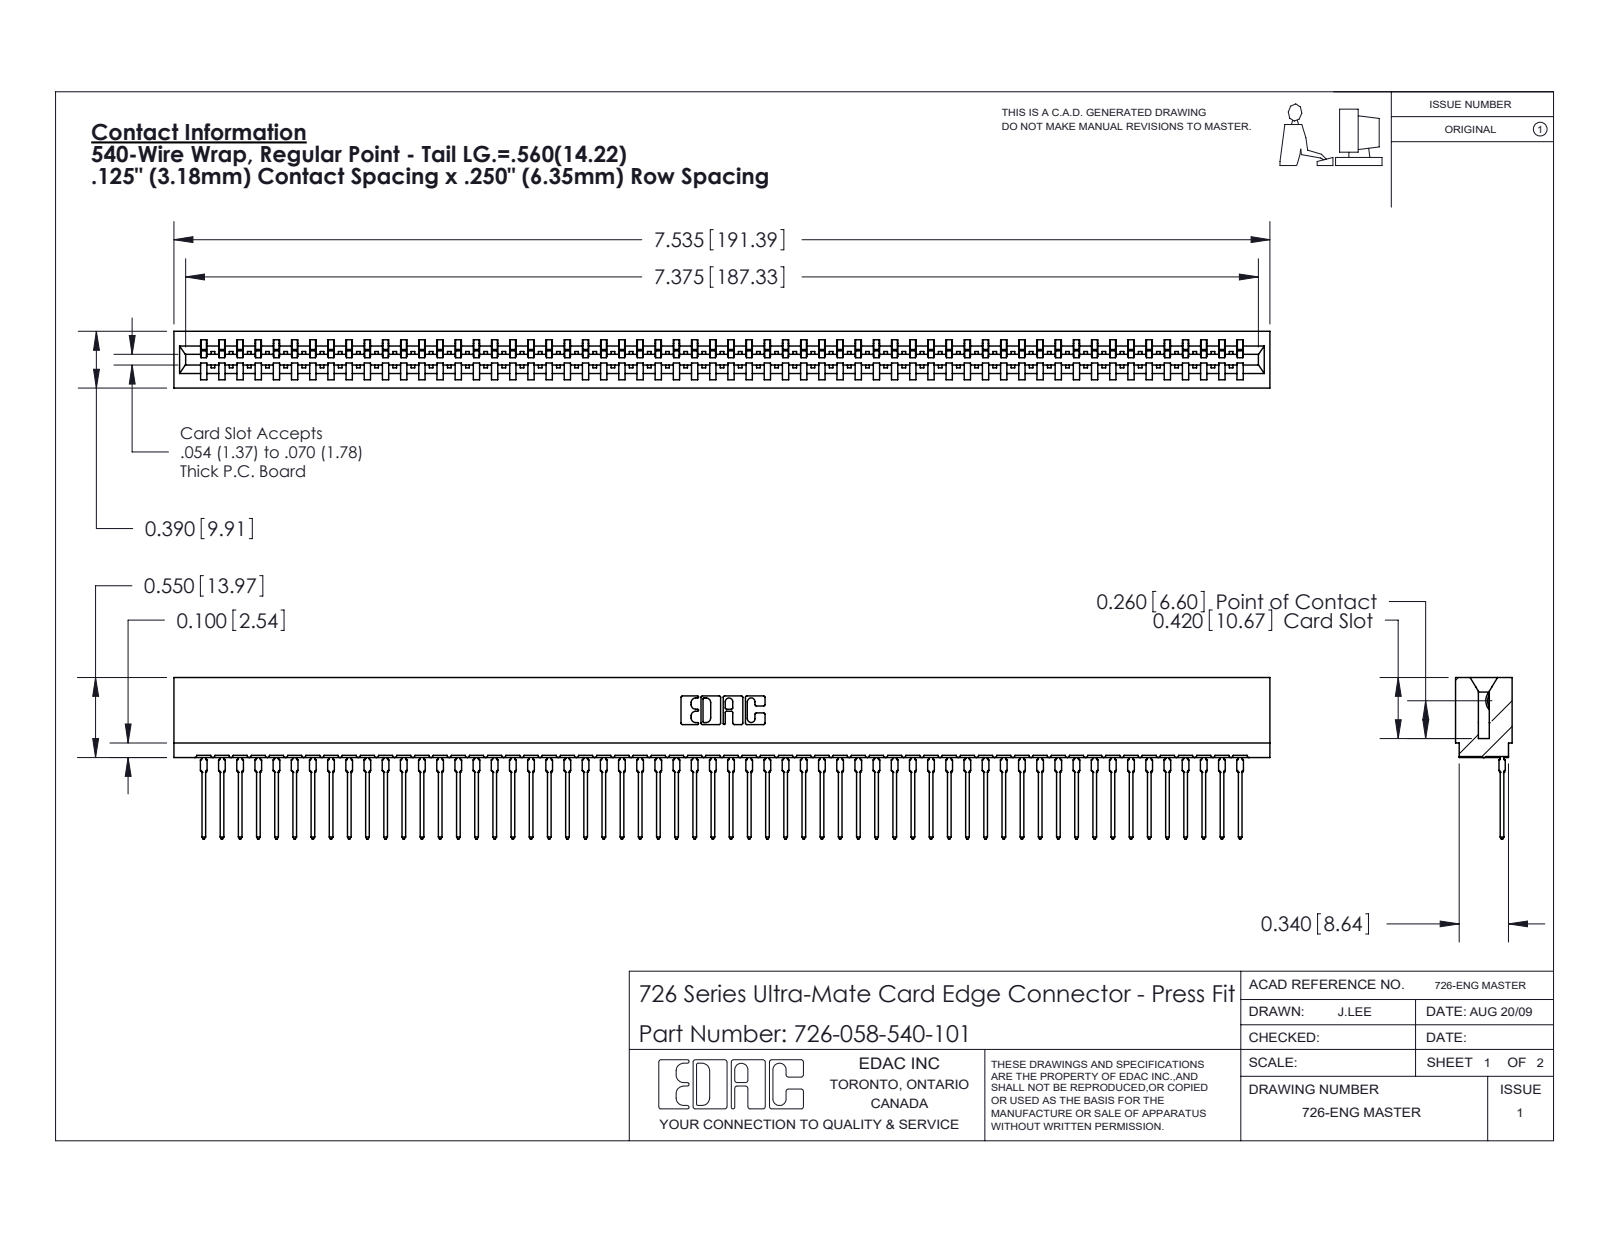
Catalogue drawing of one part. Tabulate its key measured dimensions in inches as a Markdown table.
| quantity | value |
| --- | --- |
| part name | 746-292-001_540; 726-058-540-101; 726 Part_.515 Slot Depth - 01 |
| STEP written by | SolidWorks 2020 (CONFIG_CONTROL_DESIGN) |
| units | inches |
| bodies | 59 solids, 6361 faces (3709 planar, 1144 cylindrical, 1508 other) |
| overall size | 7.535 × 1.109 × 0.39 |
| volume | 1.046 in³ |
| surface area | 41.97 in² |
| partial cylindrical surfaces (radius × count) | 0.021 × 116, 0.015 × 59, 0.01 × 22, 0.007 × 6, 0.031 × 6, 0.005 × 4, 0.011 × 4, 0.026 × 3 |
| main face-to-face distances | 0.057, 0.333, 0.39, 0.025, 0.307, 0.25, 0.275, 0.083, 0.365, 0.032 |
